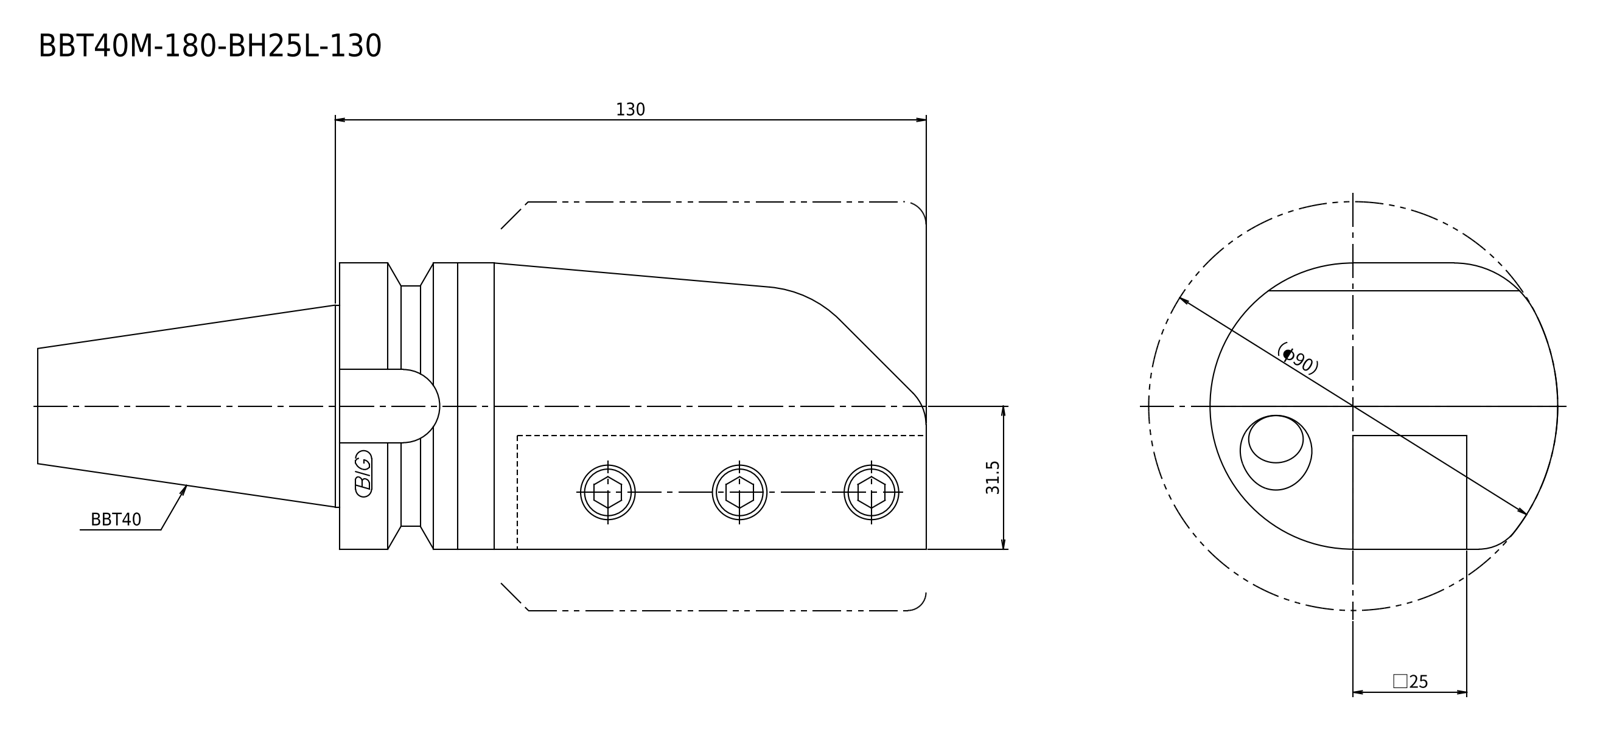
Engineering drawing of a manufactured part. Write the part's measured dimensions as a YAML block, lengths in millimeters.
part_name: "240[2]"
step_written_by: "Kubotek KeyCreator 2011 V10.0.2 (22737) (automotive_design)"
units: millimeters
bodies: {solids: 1, faces: 21, planar: 11, cylindrical: 6, other: 4}
overall_size: [195.4, 76.5, 63]
volume: 462805
surface_area: 46572
round_bosses_or_shafts:
  - {diameter: 63, count: 1}
  - {diameter: 53, count: 1}
  - {diameter: 44.45, count: 1}
partial_cylinders:
  - {radius: 20, count: 1}
  - {radius: 45, count: 1}
face_to_face_distances: [25, 129, 95, 34, 90, 5, 39, 195.4, 105.4, 100.4]
